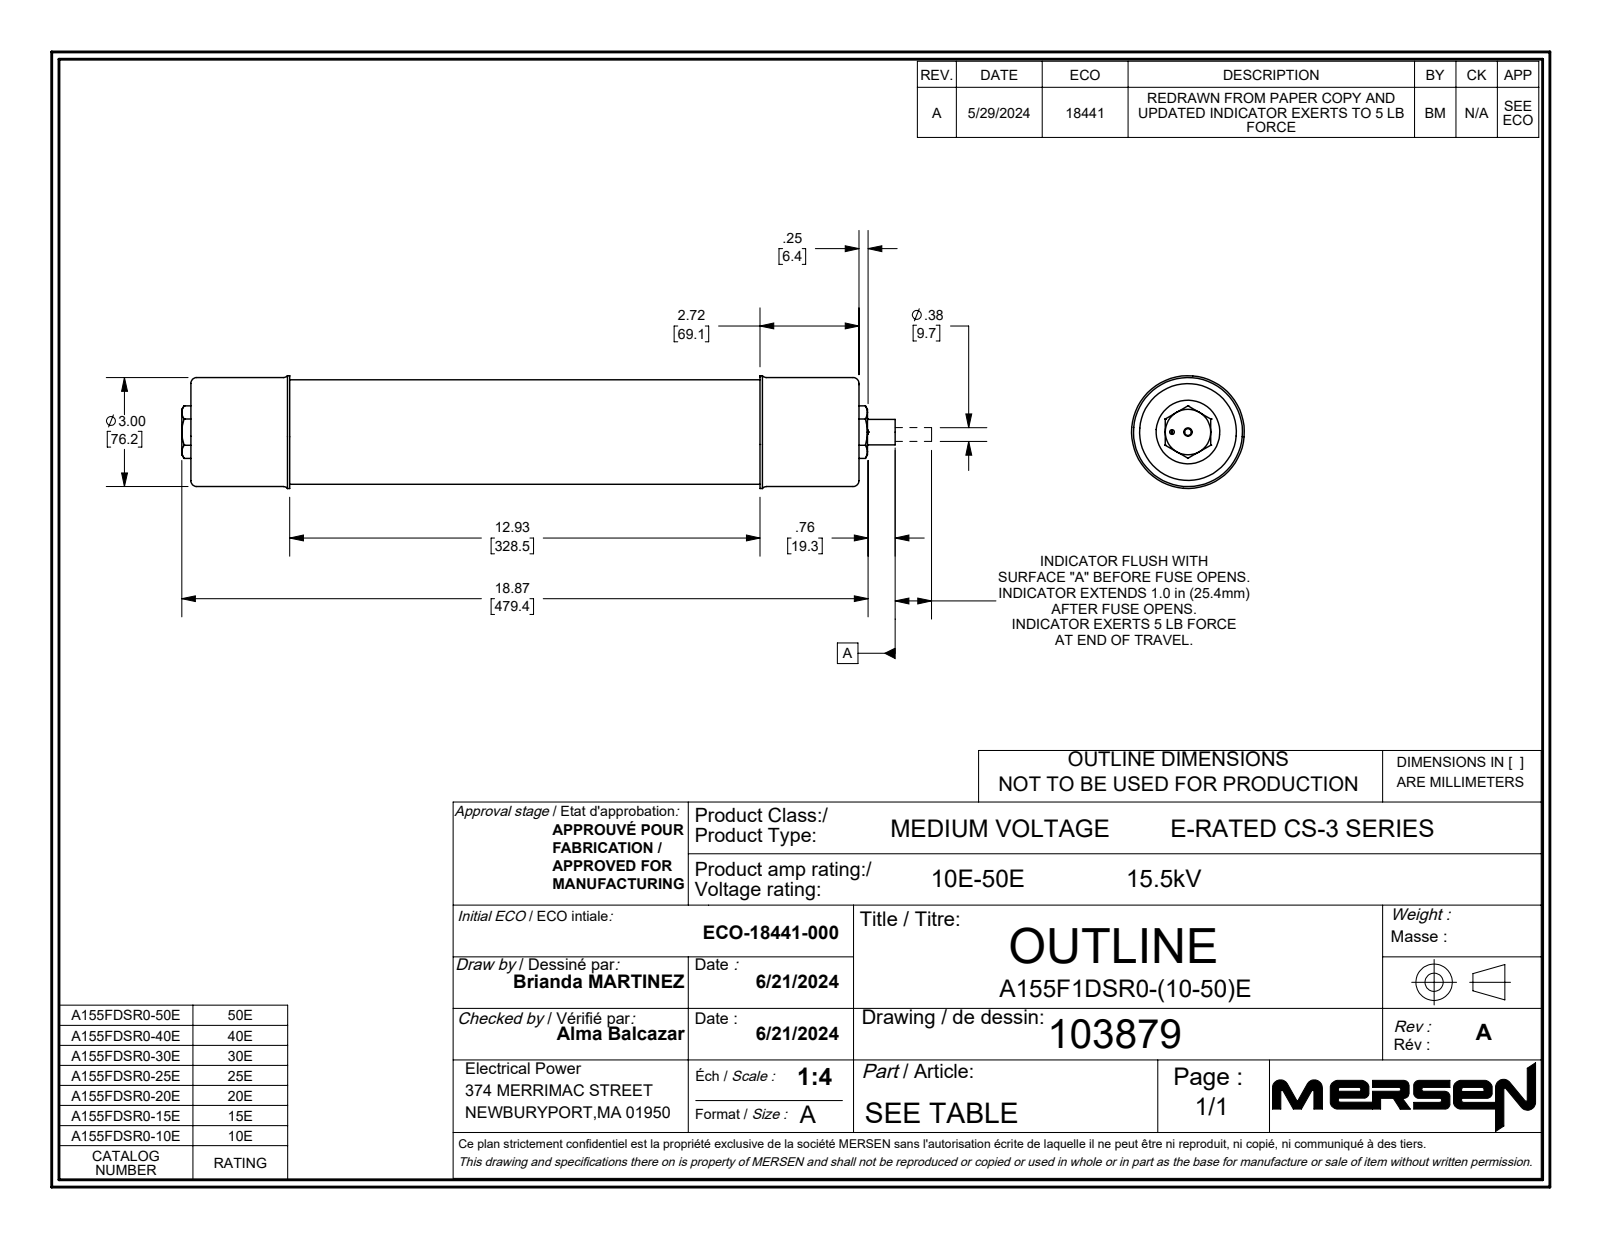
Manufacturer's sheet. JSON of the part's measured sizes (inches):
{"part_name": "105928_105928_CRIMPED; 103879; 130078_-005; 11688 (+4 more)", "step_written_by": "SolidWorks 2021 (AUTOMOTIVE_DESIGN)", "units": "inches", "bodies": {"solids": 6, "faces": 225, "planar": 55, "cylindrical": 97, "other": 73}, "overall_size": [19.617, 3.1, 3.1], "volume_in3": 24.41, "surface_area_in2": 457.6, "round_holes": [[0.125, 12], [0.129, 2], [0.069, 1], [0.188, 1], [0.391, 1], [0.465, 1], [0.512, 1], [0.906, 1], [2.625, 1], [2.89, 1]], "round_bosses_or_shafts": [[3.1, 1], [2.998, 1], [2.875, 1], [1.25, 1], [0.875, 1], [0.874, 1], [0.78, 1], [0.7, 1]], "face_to_face_distances": [0.054, 18.195, 0.084, 18.165, 0.03, 18.111, 18.249, 18.141, 0.016, 18.233], "hole_center_spacings": [17.521, 0.438, 0.876]}
